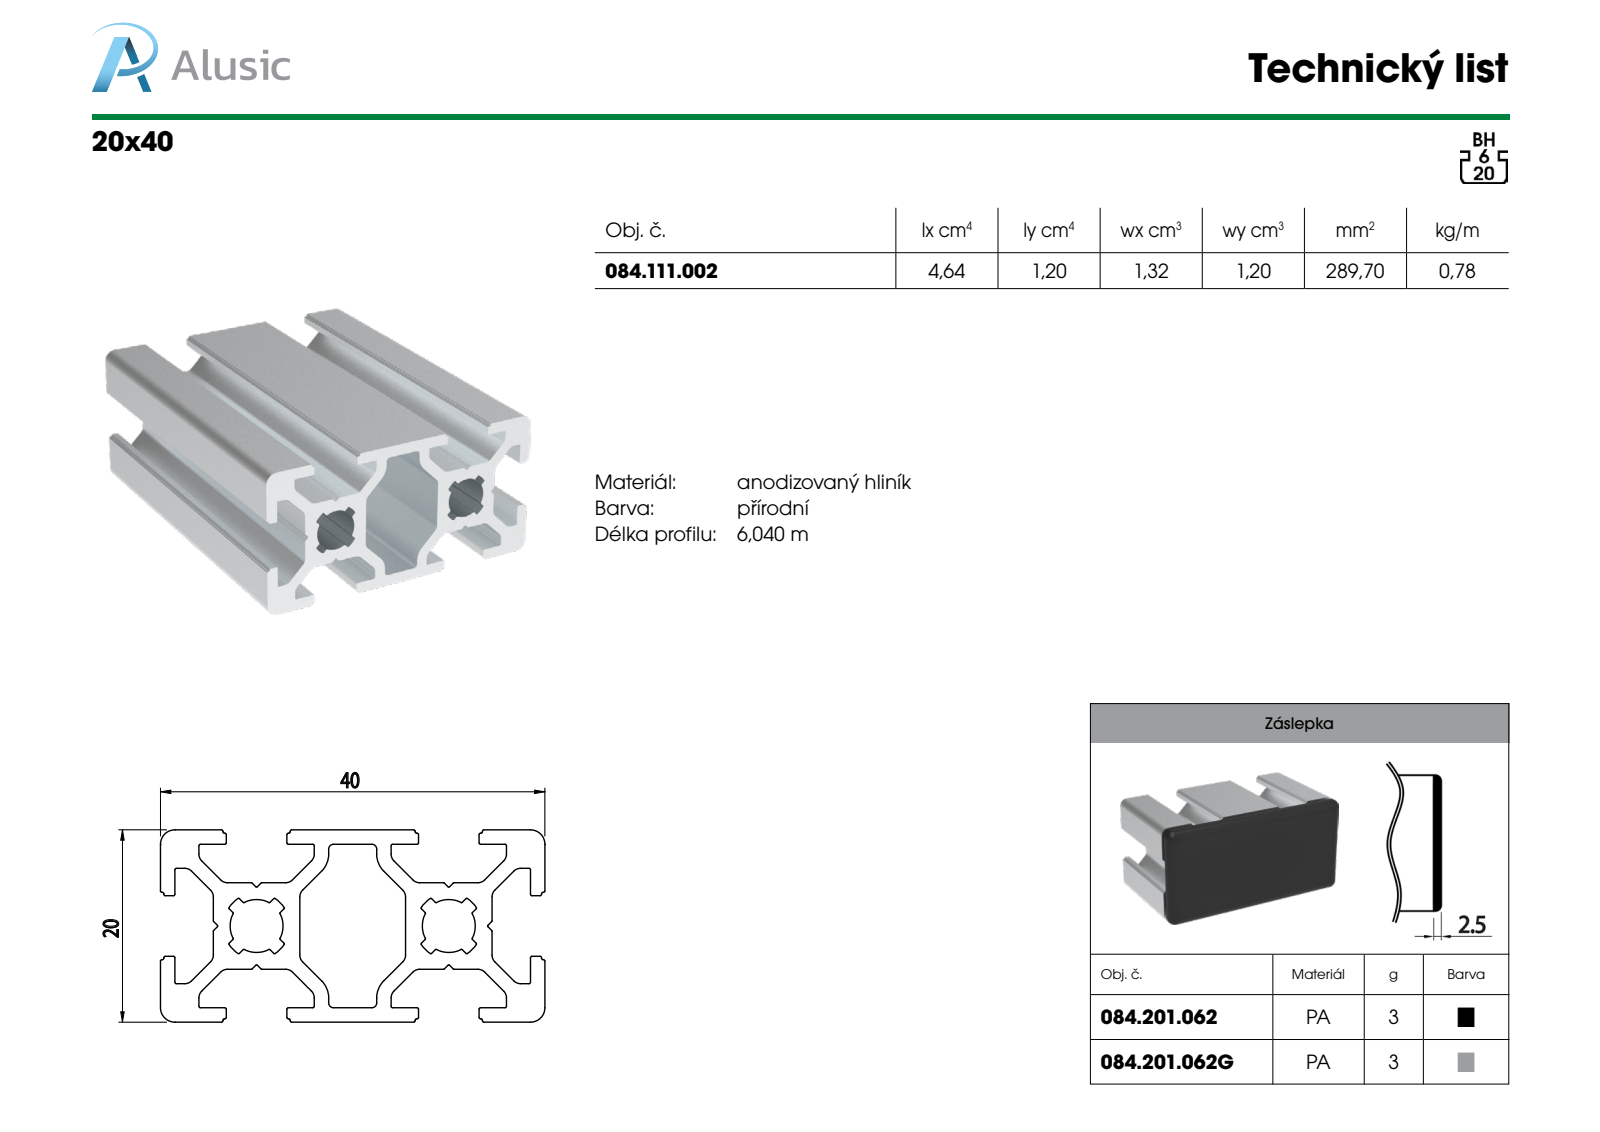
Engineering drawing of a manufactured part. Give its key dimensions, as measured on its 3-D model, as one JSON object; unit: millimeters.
{"part_name": "084.111.002", "step_written_by": "SolidWorks 2018 (AUTOMOTIVE_DESIGN)", "units": "millimeters", "bodies": {"solids": 1, "faces": 313, "planar": 136, "cylindrical": 177, "other": 0}, "overall_size": [100, 40, 20], "volume_mm3": 28970, "surface_area_mm2": 32971, "partial_cylinders_radius": [[0.15, 60], [0.1, 50], [1, 28], [0.5, 4], [1.5, 4], [2.5, 4], [2.75, 2], [3.45, 2]], "face_to_face_distances": [1.5, 20, 14.5, 4, 18.5, 13, 5.5, 14.14, 9, 17]}
